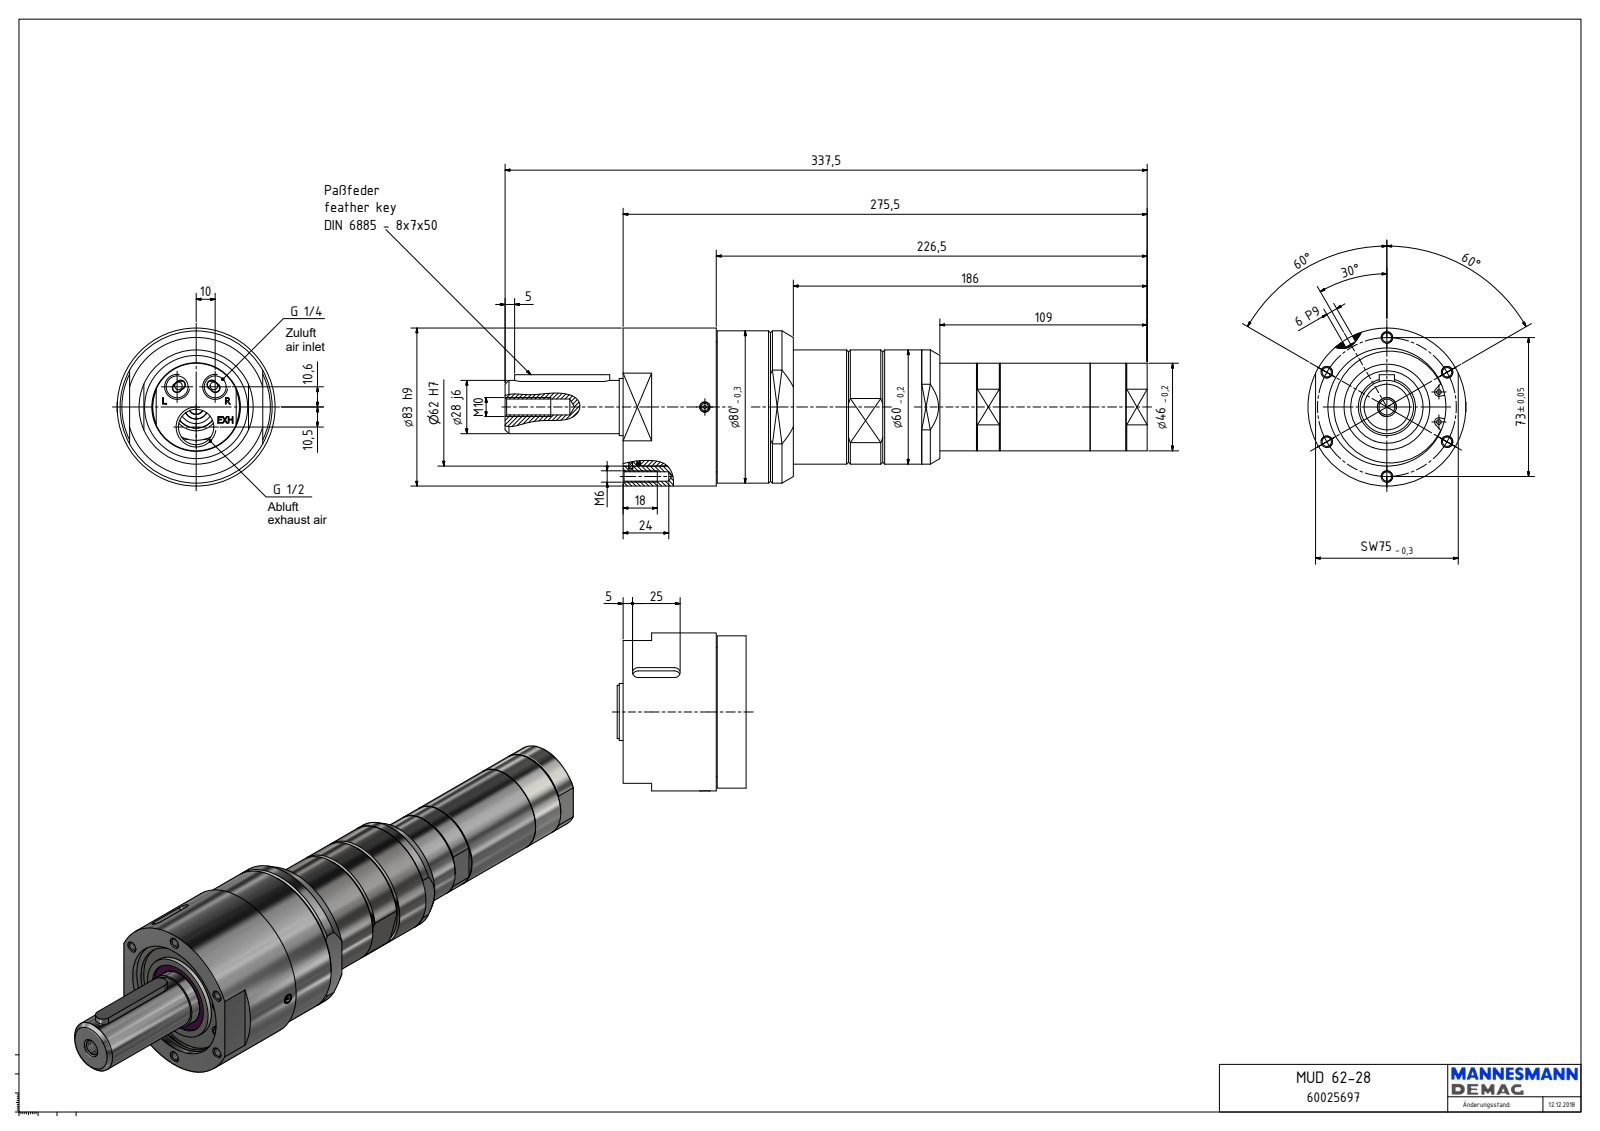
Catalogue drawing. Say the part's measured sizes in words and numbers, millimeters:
The part is named "MUD 62-28_60025697". Its 3-D file was written by "Autodesk Inventor 2018 (AUTOMOTIVE_DESIGN)". It is 1 solid with 282 faces: 138 planar, 75 cylindrical and 69 other. Overall it measures 337.5 by 83 by 83 millimeters. Its volume is 873 701 cubic millimeters and its surface area 86 322 square millimeters. Round holes: 6 of diameter 4.92, 3 of diameter 1.55, 2 of diameter 2.5, 2 of diameter 4, 2 of diameter 5.5, 2 of diameter 11.45, 1 of diameter 8.38, 1 of diameter 18.63, 1 of diameter 36.5, 1 of diameter 38, 1 of diameter 40, 1 of diameter 46.5. Round bosses or shafts: 2 of diameter 5, 2 of diameter 3.6, 1 of diameter 83, 1 of diameter 80, 1 of diameter 68.18, 1 of diameter 67, 1 of diameter 60, 1 of diameter 46. Partial cylindrical surfaces (rounded edges, fillets, slot ends): 2 of radius 2.25, 2 of radius 3, 2 of radius 4, 2 of radius 5, 1 of radius 25.13, 1 of radius 32.91. The main face-to-face distances are 0.5, 49, 2.5, 5, 44, 89.5, 84.5, 40.5, 49.5, 44.5. The hole center spacings are 36.5, 63.22, 73, 11.21, 14.57, 22.92, 23.35, 26.48.
